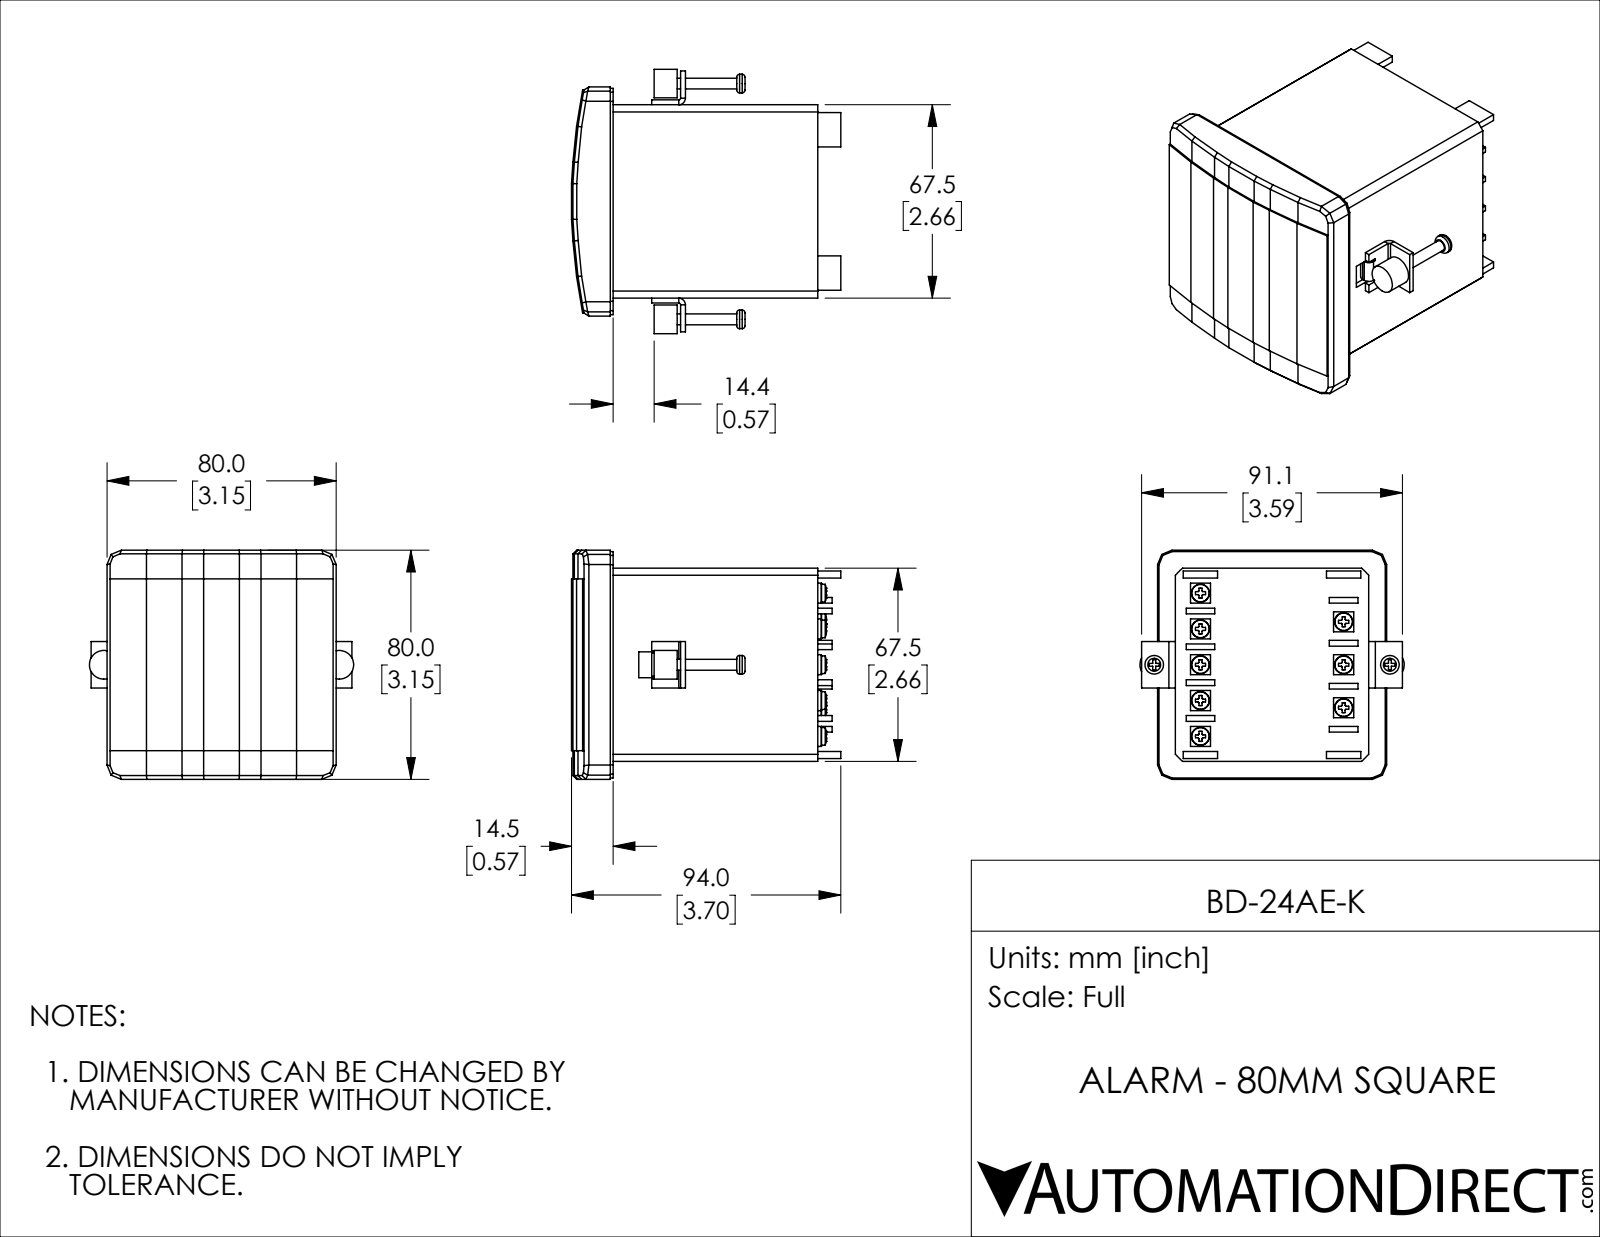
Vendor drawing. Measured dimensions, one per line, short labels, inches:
name: BD-24AE-K
written by: SolidWorks 2018 (AUTOMOTIVE_DESIGN)
unit: in
bodies: 5 solids, 493 faces (366 planar, 88 cylindrical, 39 other)
size: 3.701 × 3.634 × 3.15
volume: 25.1 in³; area: 65.35 in²
holes: 2× ⌀0.152
bosses: 8× ⌀0.248, 2× ⌀0.394, 2× ⌀0.256, 2× ⌀0.15
rounds: 8× R0.038, 8× R0.684, 6× R0.024, 6× R0.091, 1× R1.811
face distances: 2.657, 0.246, 2.904, 2.815, 3.15, 0.02, 0.571, 0.197, 3.386, 0.039
hole spacings: 3.24
